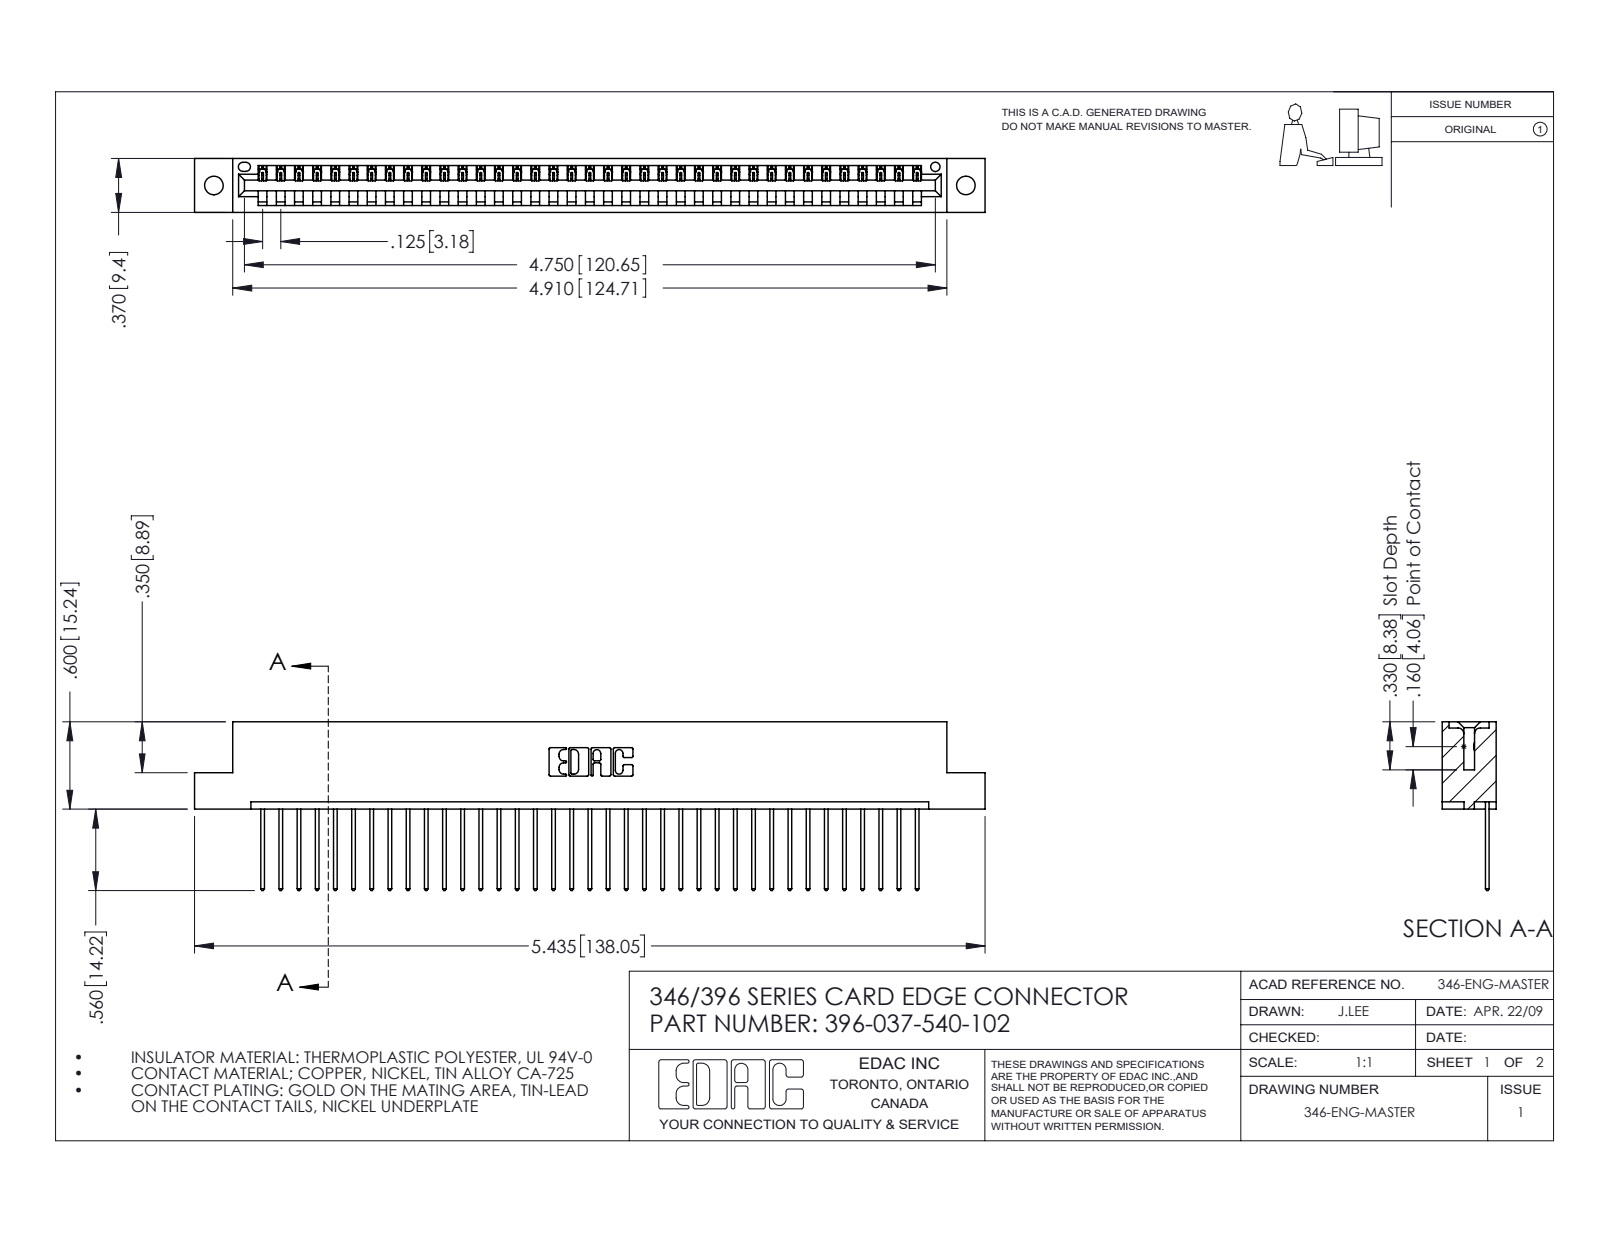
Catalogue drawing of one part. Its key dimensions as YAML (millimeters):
part_name: "345-292-001_345-293-140; 346 Part_Flush Mounting Lugs - 0.128 Dia; 396-037-540-102"
step_written_by: "SolidWorks 2016 (CONFIG_CONTROL_DESIGN)"
units: millimeters
bodies: {solids: 38, faces: 2268, planar: 1556, cylindrical: 712, other: 0}
overall_size: [138, 29.5, 9.4]
volume: 13200
surface_area: 16530
round_holes:
  - {diameter: 3.3, count: 2}
  - {diameter: 1.6, count: 1}
partial_cylinders:
  - {radius: 0.2, count: 74}
  - {radius: 0.3, count: 74}
  - {radius: 0.3, count: 22}
  - {radius: 0.2, count: 6}
  - {radius: 0.8, count: 6}
  - {radius: 0.7, count: 3}
  - {radius: 0.8, count: 2}
  - {radius: 1, count: 2}
face_to_face_distances: [1.2, 8.2, 9.4, 6.4, 1.8, 7.6, 0.6, 3.8, 5.6, 2.5]
hole_center_spacings: [6.2, 126, 131.3]
